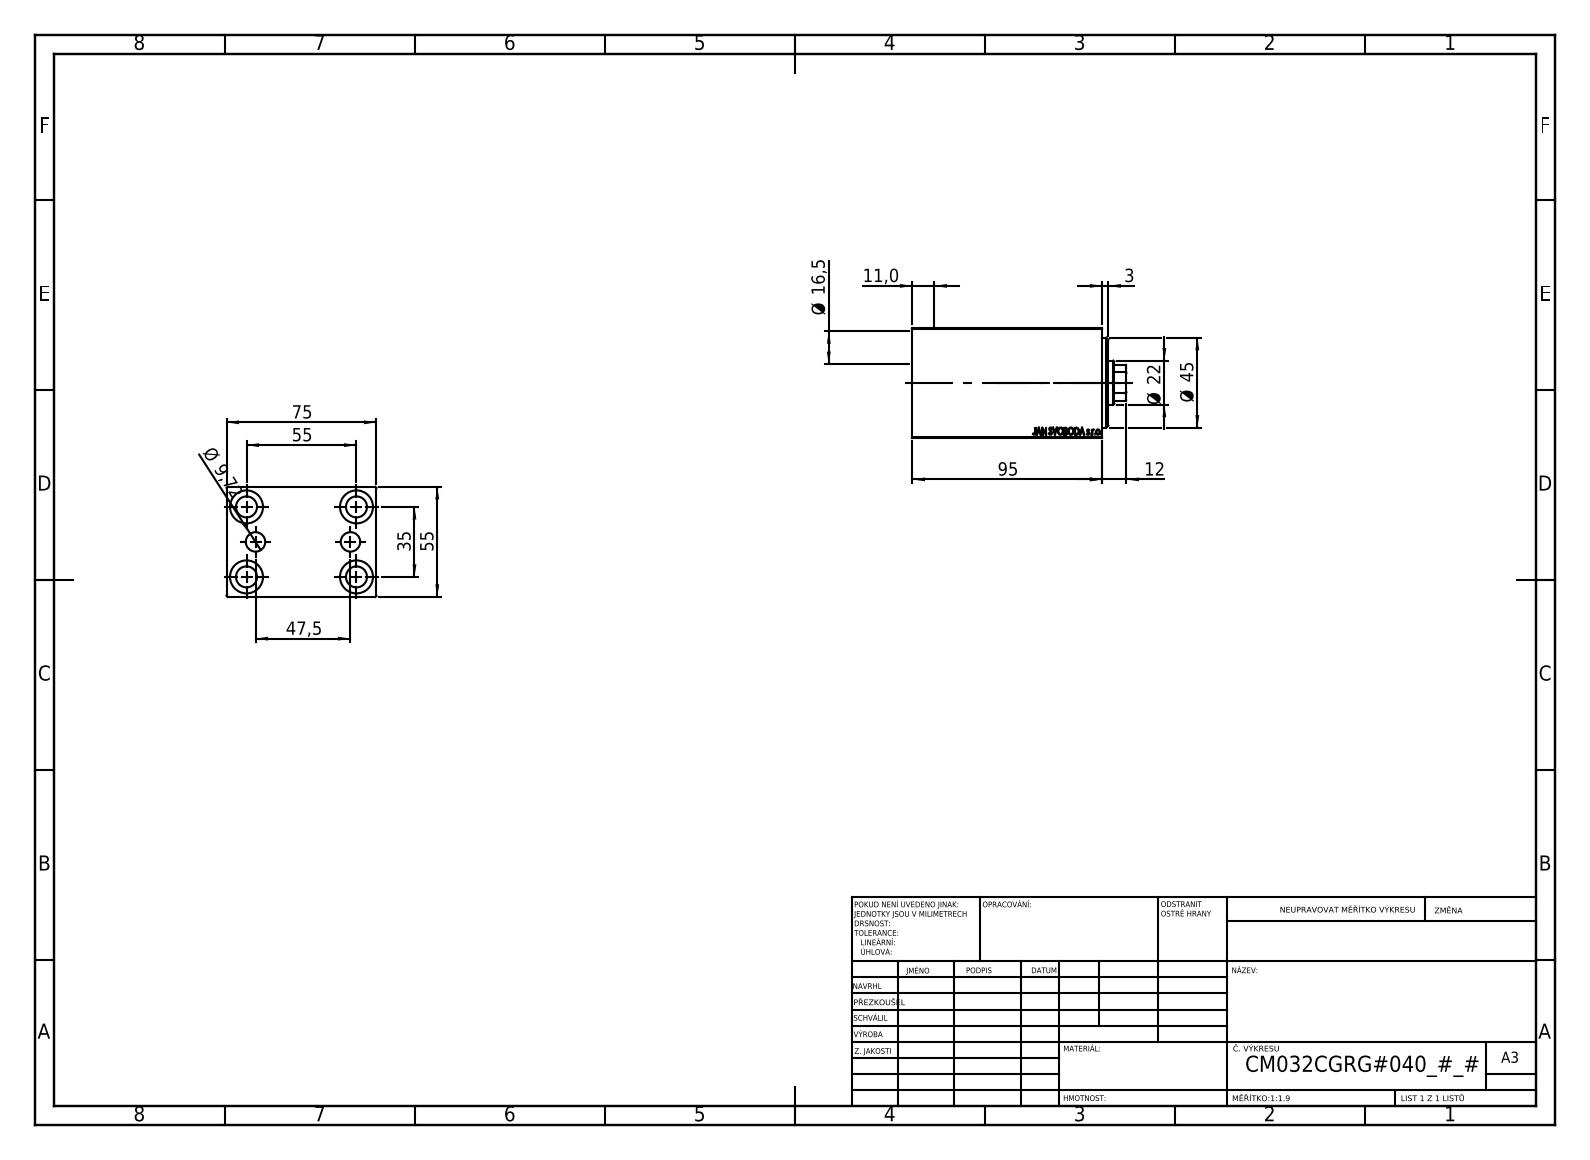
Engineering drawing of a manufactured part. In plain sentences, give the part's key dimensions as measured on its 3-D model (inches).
The part is named "V450CM_C_VCP; V450CM_VC_B; V450CM_C_Body". Its 3-D file was written by "SolidWorks 2019 (CONFIG_CONTROL_DESIGN)". It is 3 solids with 852 faces: 406 planar, 52 cylindrical and 394 other. Overall it measures 4.213 by 2.953 by 2.165 inches. Its volume is 20.45 cubic inches and its surface area 110 square inches. Round holes: 5 of diameter 0.413, 4 of diameter 0.65, 2 of diameter 0.383, 1 of diameter 0.866, 1 of diameter 1.004, 1 of diameter 1.26, 1 of diameter 1.339, 1 of diameter 1.772. Partial cylindrical surfaces (rounded edges, fillets, slot ends): 1 of radius 0.413. The main face-to-face distances are 2.165, 2.953, 0.394, 3.346, 3.74, 3.543, 0.197, 3.15, 2.874, 0.433. The hole center spacings are 1.283, 0.699, 0.711, 1.378, 2.104, 2.16, 2.165, 2.567.
